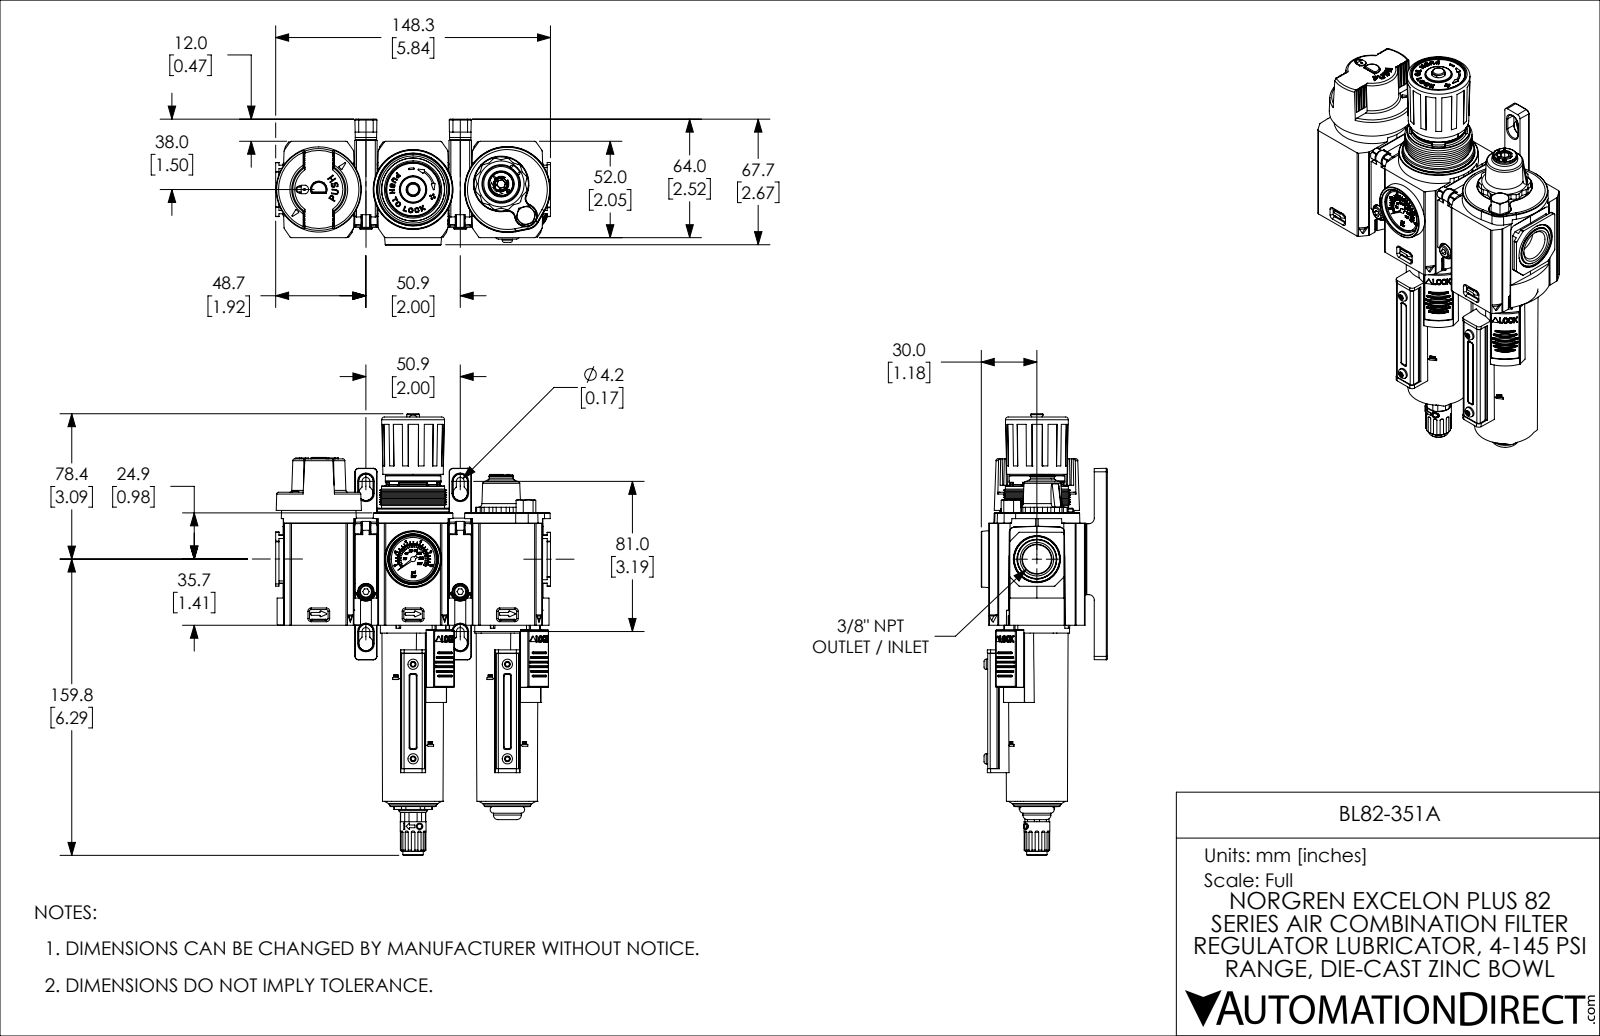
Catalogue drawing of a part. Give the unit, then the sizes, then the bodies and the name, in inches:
Units: inches
Overall size (bounding box): 9.379 × 5.839 × 2.676
Round holes (diameter × count): ⌀0.097 ×4, ⌀0.306 ×4, ⌀0.039 ×2, ⌀0.128 ×2, ⌀0.138 ×2, ⌀0.175 ×2, ⌀0.187 ×2, ⌀0.628 ×2, ⌀0.098 ×1, ⌀0.106 ×1, ⌀0.128 ×1, ⌀0.197 ×1
Round bosses / shafts (diameter × count): ⌀0.276 ×4, ⌀0.217 ×4, ⌀1.388 ×2, ⌀1.356 ×2, ⌀1.291 ×2, ⌀1.257 ×2, ⌀0.24 ×2, ⌀0.224 ×2
Partial cylindrical surfaces — rounded edges, fillets, slot ends (radius × count): R0.039 ×164, R0.02 ×148, R0.01 ×27, R0.006 ×26, R0.009 ×25, R0.011 ×25, R0.012 ×25, R0.03 ×25
Main face-to-face distances: 0.059, 2.004, 1.988, 2.002, 2.047, 1.929, 4.004, 1.352, 0.182, 0.152
Hole centre spacings: 0.63, 2.004, 0.554, 1.58, 0.59, 0.689, 1.002, 1.091
Volume: 37.37 in³ · Surface area: 327.7 in²
Bodies: 20 solids, 5469 faces (2304 planar, 2204 cylindrical, 961 other)
Part name (STEP PRODUCT): BL82-351A
STEP written by: SolidWorks 2021 (CONFIG_CONTROL_DESIGN)
